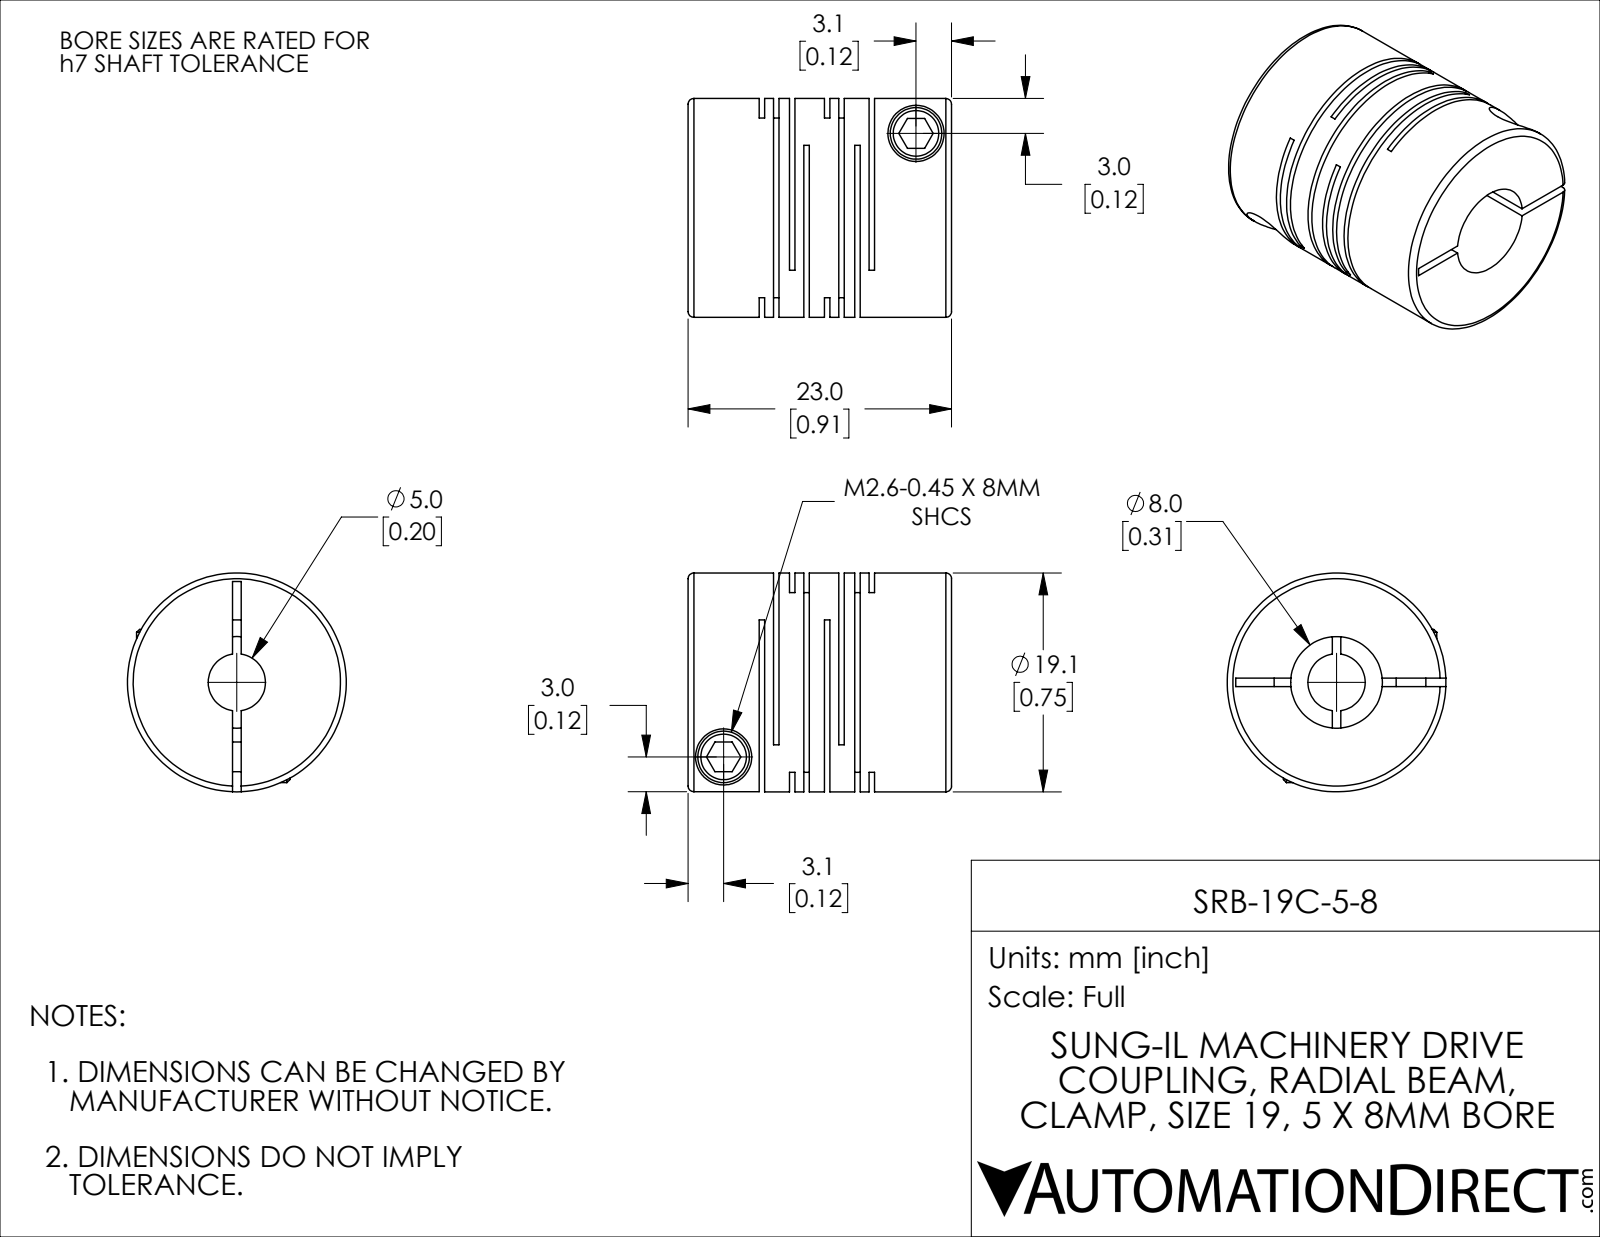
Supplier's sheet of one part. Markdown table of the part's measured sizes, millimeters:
| quantity | value |
| --- | --- |
| part name | SRB-19C-5-8 |
| STEP written by | SolidWorks 2021 (CONFIG_CONTROL_DESIGN) |
| units | millimeters |
| bodies | 1 solid, 114 faces (60 planar, 42 cylindrical, 12 other) |
| overall size | 23 × 19.1 × 19.1 |
| volume | 4 655 mm³ |
| surface area | 5 729 mm² |
| round holes (diameter × count) | 2.6 × 2, 4.9 × 2, 5 × 1, 8 × 1 |
| round bosses / shafts (diameter × count) | 4.5 × 2, 19.1 × 1 |
| main face-to-face distances | 5.7, 0.48, 1.25, 2.65, 2.17, 3.05, 5.22, 4.45, 0.77, 1.4 |
